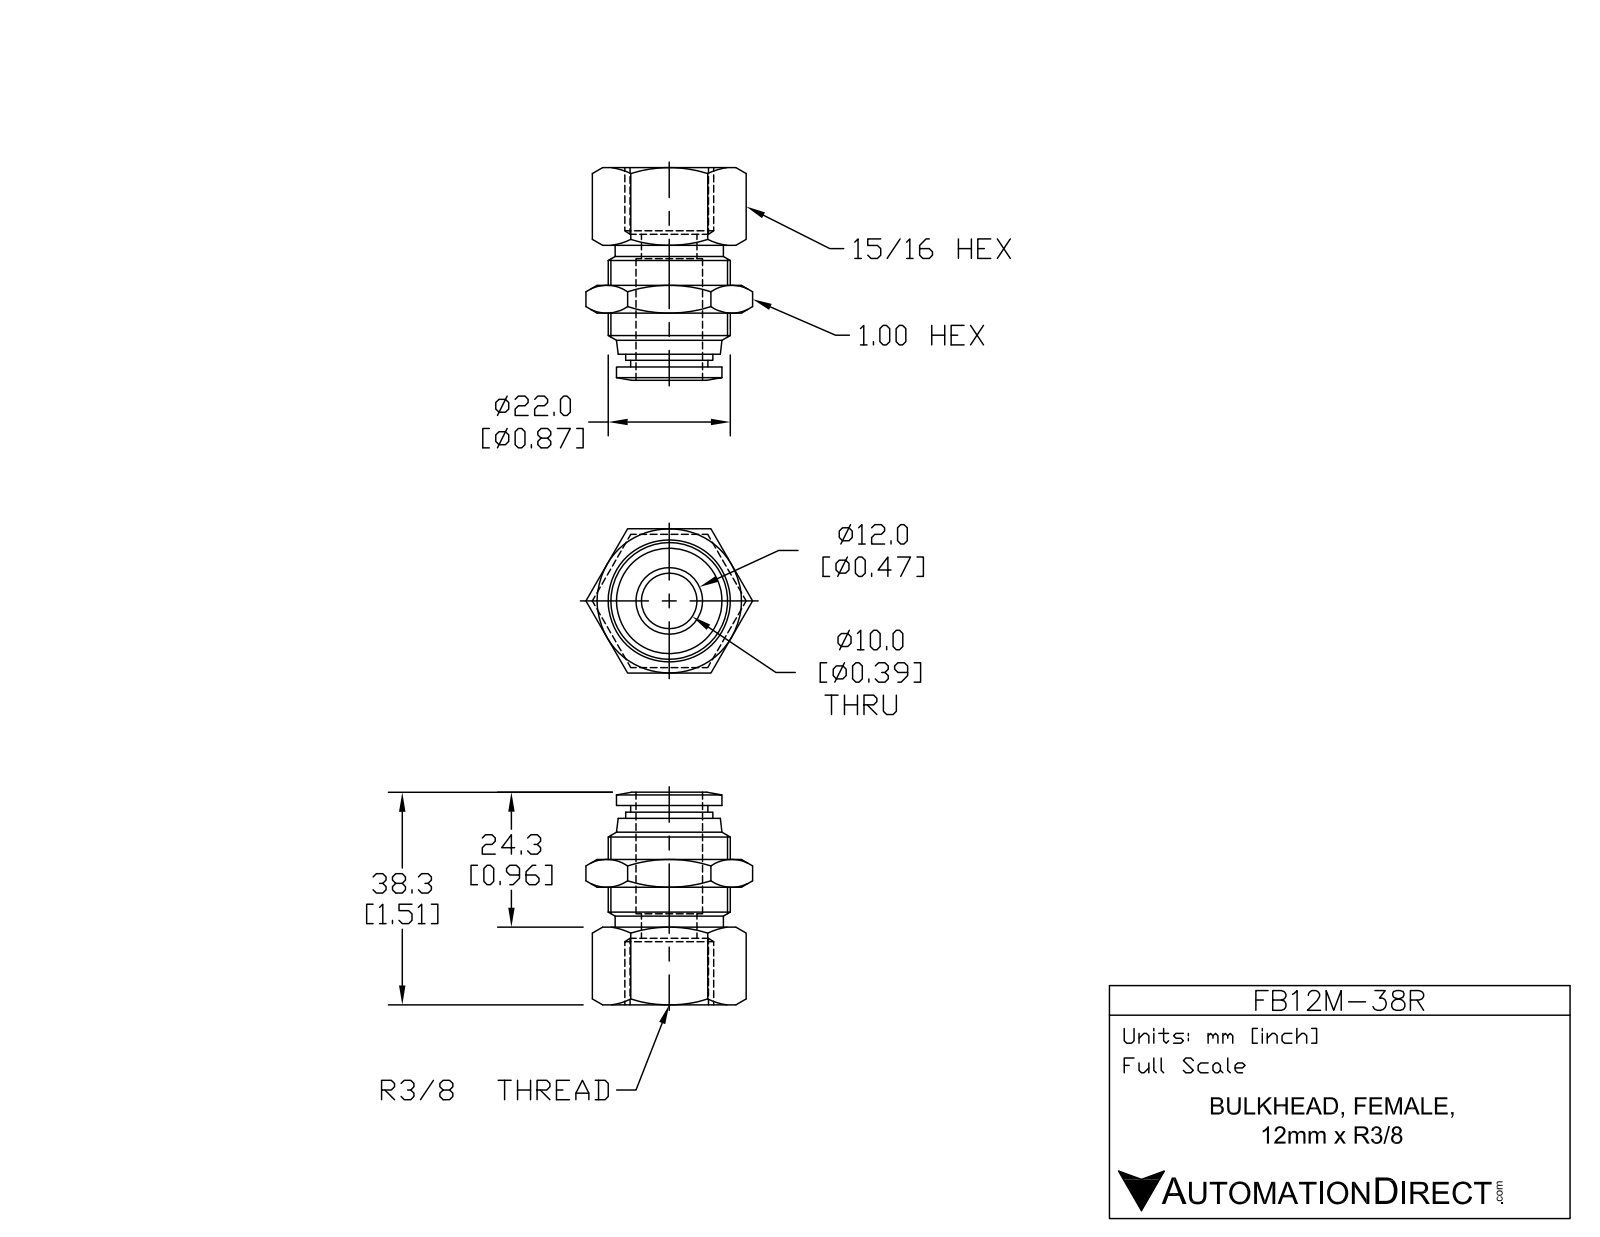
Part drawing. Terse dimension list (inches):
name: FB12M-38R
written by: SolidWorks 2015 (AUTOMOTIVE_DESIGN)
unit: in
bodies: 1 solid, 78 faces (22 planar, 16 cylindrical, 40 other)
size: 1.508 × 1.182 × 1.024
volume: 0.64 in³; area: 9.078 in²
holes: 1× ⌀0.394, 1× ⌀0.484
bosses: 1× ⌀0.866, 1× ⌀0.768, 1× ⌀0.748, 1× ⌀0.618, 1× ⌀0.547
face distances: 0.945, 0.039, 0.984, 1.024, 0.551, 0.834, 0.283, 1.031, 0.48, 0.197
